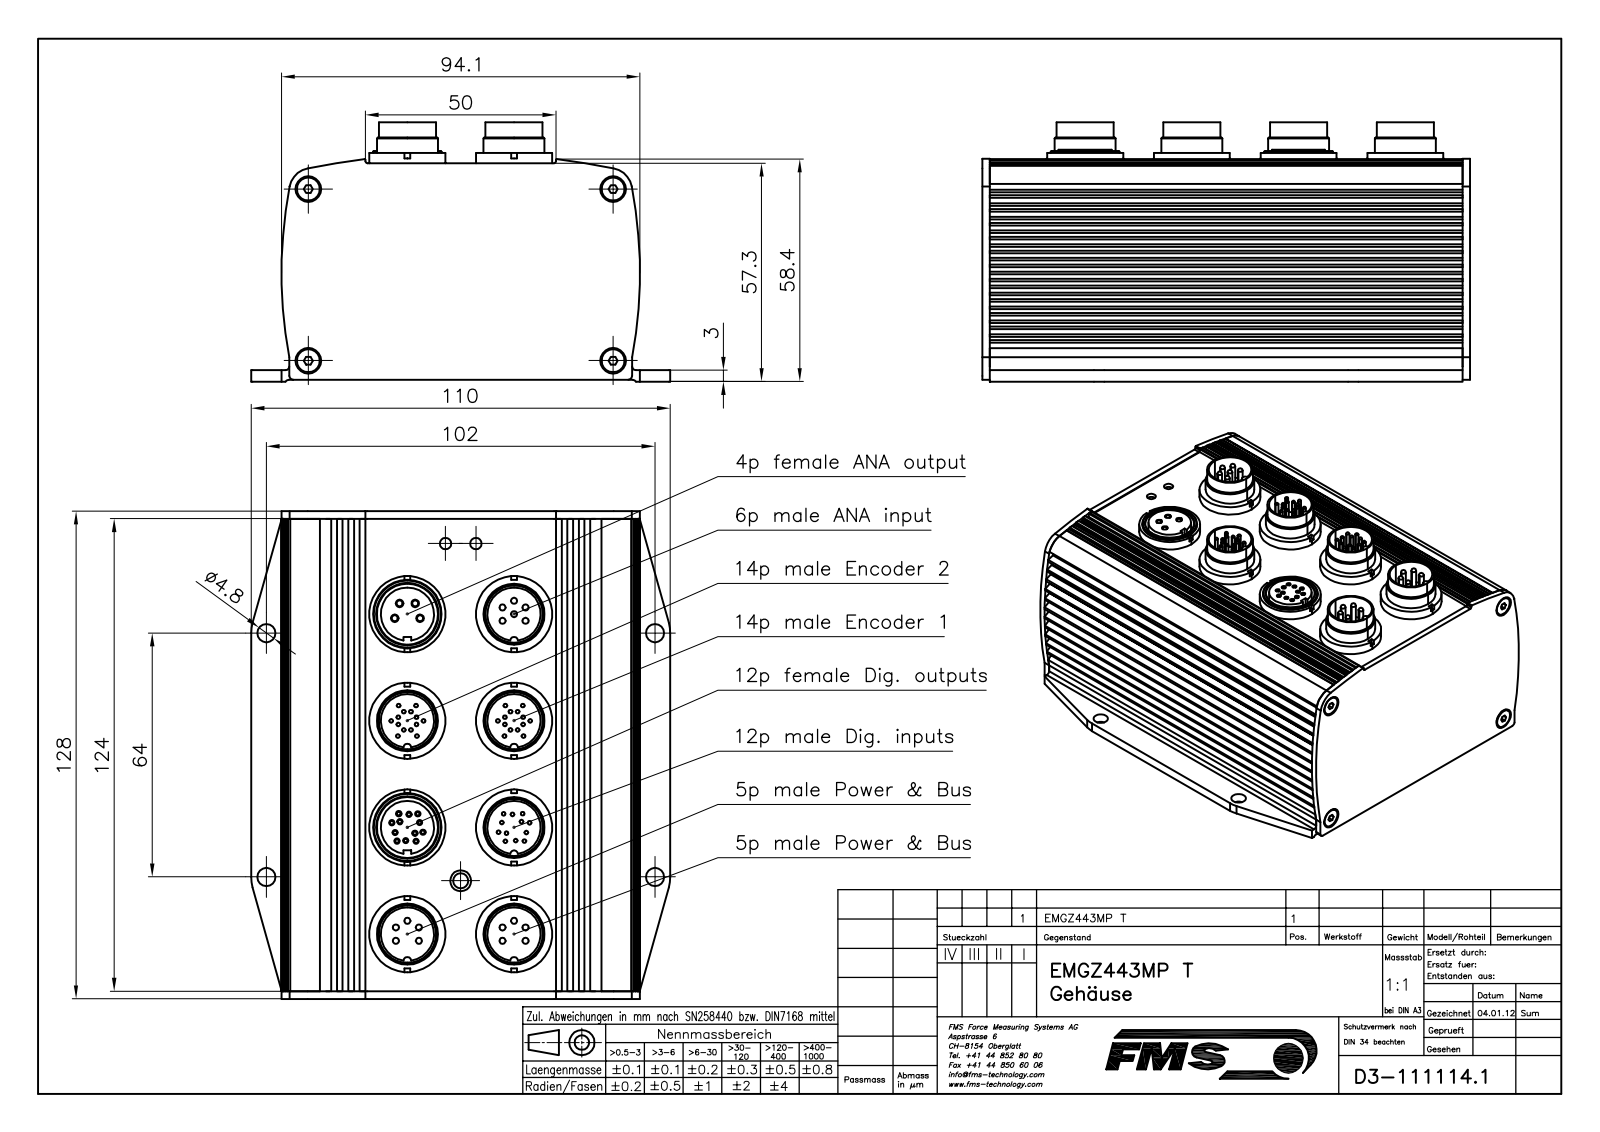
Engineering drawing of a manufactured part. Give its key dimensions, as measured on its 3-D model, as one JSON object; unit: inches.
{"part_name": "E1111141; E1111143; EINPRESSGEWINDEBOLZEN_M4X10; FLANSCHSTECKER_09-0115-89-05 (+8 more)", "step_written_by": "Mechanical Desktop 2009 (CONFIG_CONTROL_DESIGN)", "units": "inches", "bodies": {"solids": 37, "faces": 1641, "planar": 564, "cylindrical": 841, "other": 236}, "overall_size": [5.039, 4.331, 2.677], "volume_in3": 8.984, "surface_area_in2": 198.9, "round_holes": [[0.024, 52], [0.039, 12], [0.63, 8], [0.551, 6], [0.709, 6], [0.102, 5], [0.063, 4], [0.126, 4], [0.189, 4], [0.118, 2]], "round_bosses_or_shafts": [[0.028, 52], [0.039, 40], [0.043, 20], [0.063, 16], [0.787, 8], [0.591, 6], [0.571, 6], [0.531, 6]], "partial_cylinders_radius": [[0.01, 70], [0.079, 44], [0.039, 12], [0.355, 8], [0.394, 4], [0.008, 2], [0.02, 2], [0.118, 2]], "face_to_face_distances": [0.079, 2.146, 4.961, 2.067, 4.882, 2.224, 5.039, 0.098, 0.02, 0.118], "hole_center_spacings": [1.102, 0.083, 0.102, 0.197, 0.287, 0.091, 0.122, 0.168]}
